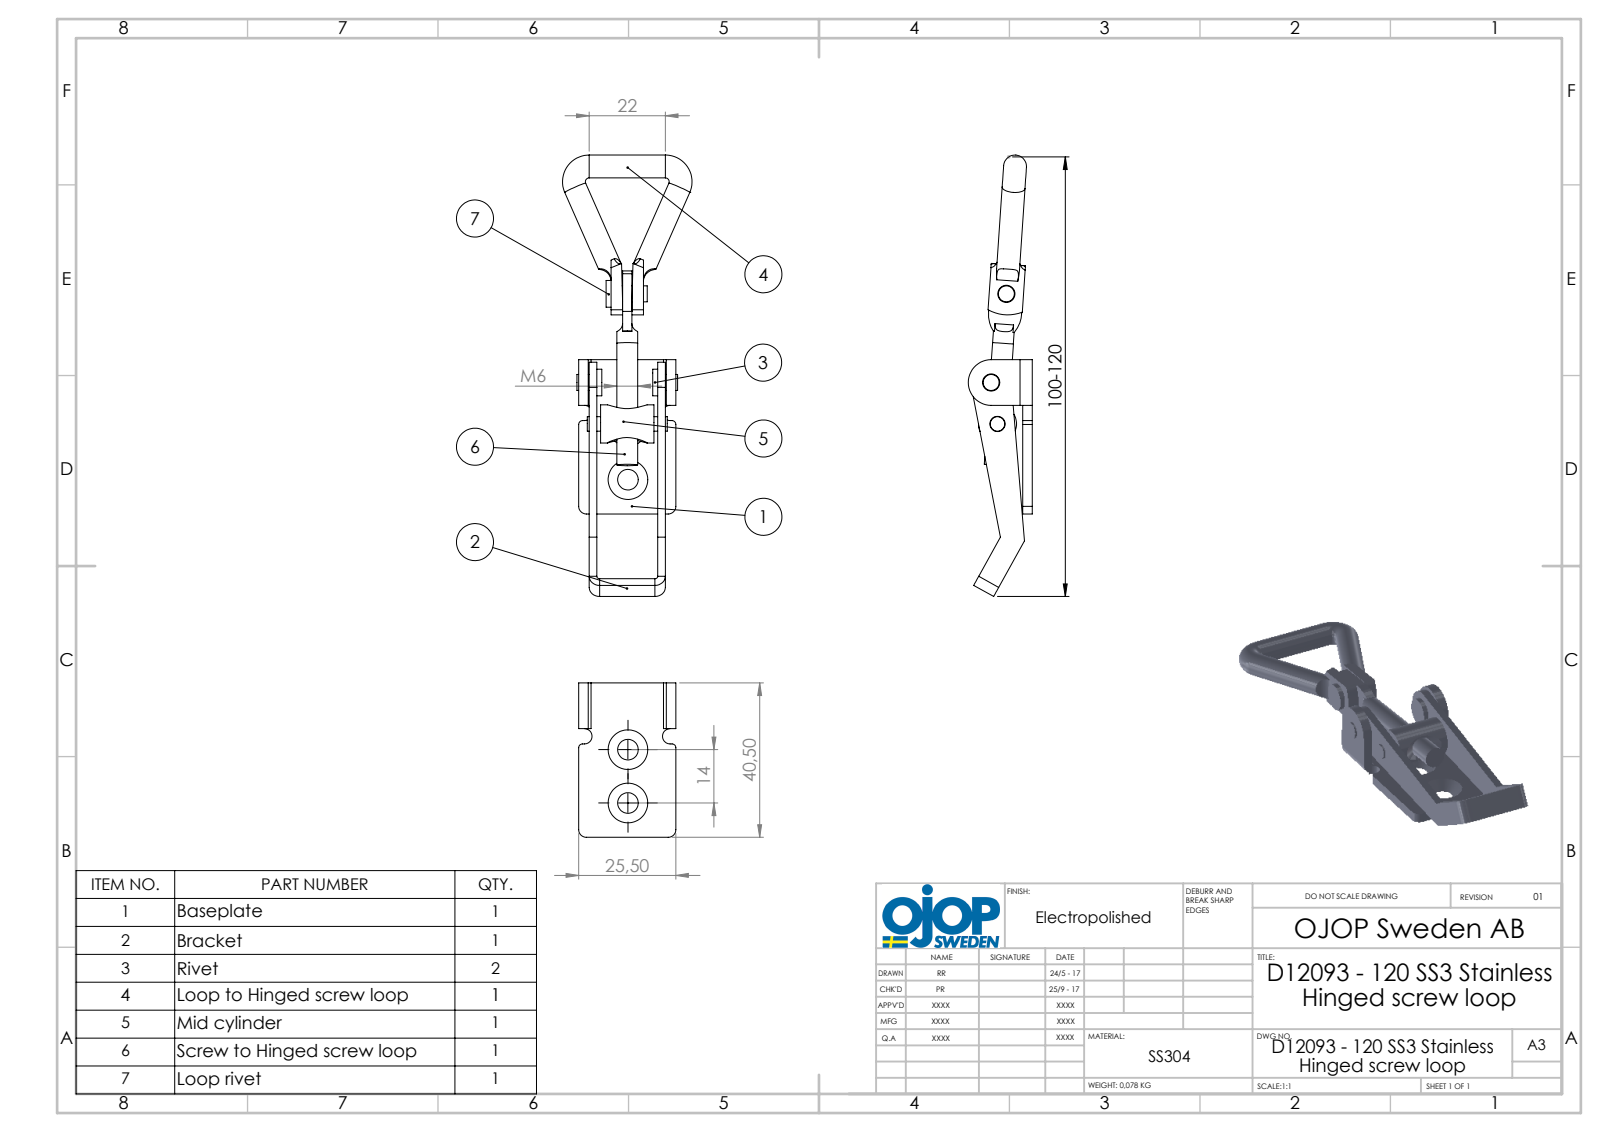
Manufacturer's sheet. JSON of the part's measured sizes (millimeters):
{"part_name": "platta; bygel; nit; ring till ledad öggla (+4 more)", "step_written_by": "SolidWorks 2015 (AUTOMOTIVE_DESIGN)", "units": "millimeters", "bodies": {"solids": 8, "faces": 181, "planar": 79, "cylindrical": 80, "other": 22}, "overall_size": [115.32, 35, 16.8], "volume_mm3": 9587, "surface_area_mm2": 10057, "round_holes": [[4.5, 2], [4, 1], [5.5, 1]], "round_bosses_or_shafts": [[5, 3], [7, 2], [4.2, 2], [10, 1], [5.47, 1], [5.46, 1], [3.8, 1]], "partial_cylinders_radius": [[2, 6], [0.74, 4], [1, 2], [2.74, 2], [3, 2], [3.24, 2], [10, 2], [5.32, 1]], "face_to_face_distances": [2.5, 2, 18, 2.75, 16, 20, 5.75, 4.75, 20.75, 22.75], "hole_center_spacings": [11.01, 23.59, 34.21]}
